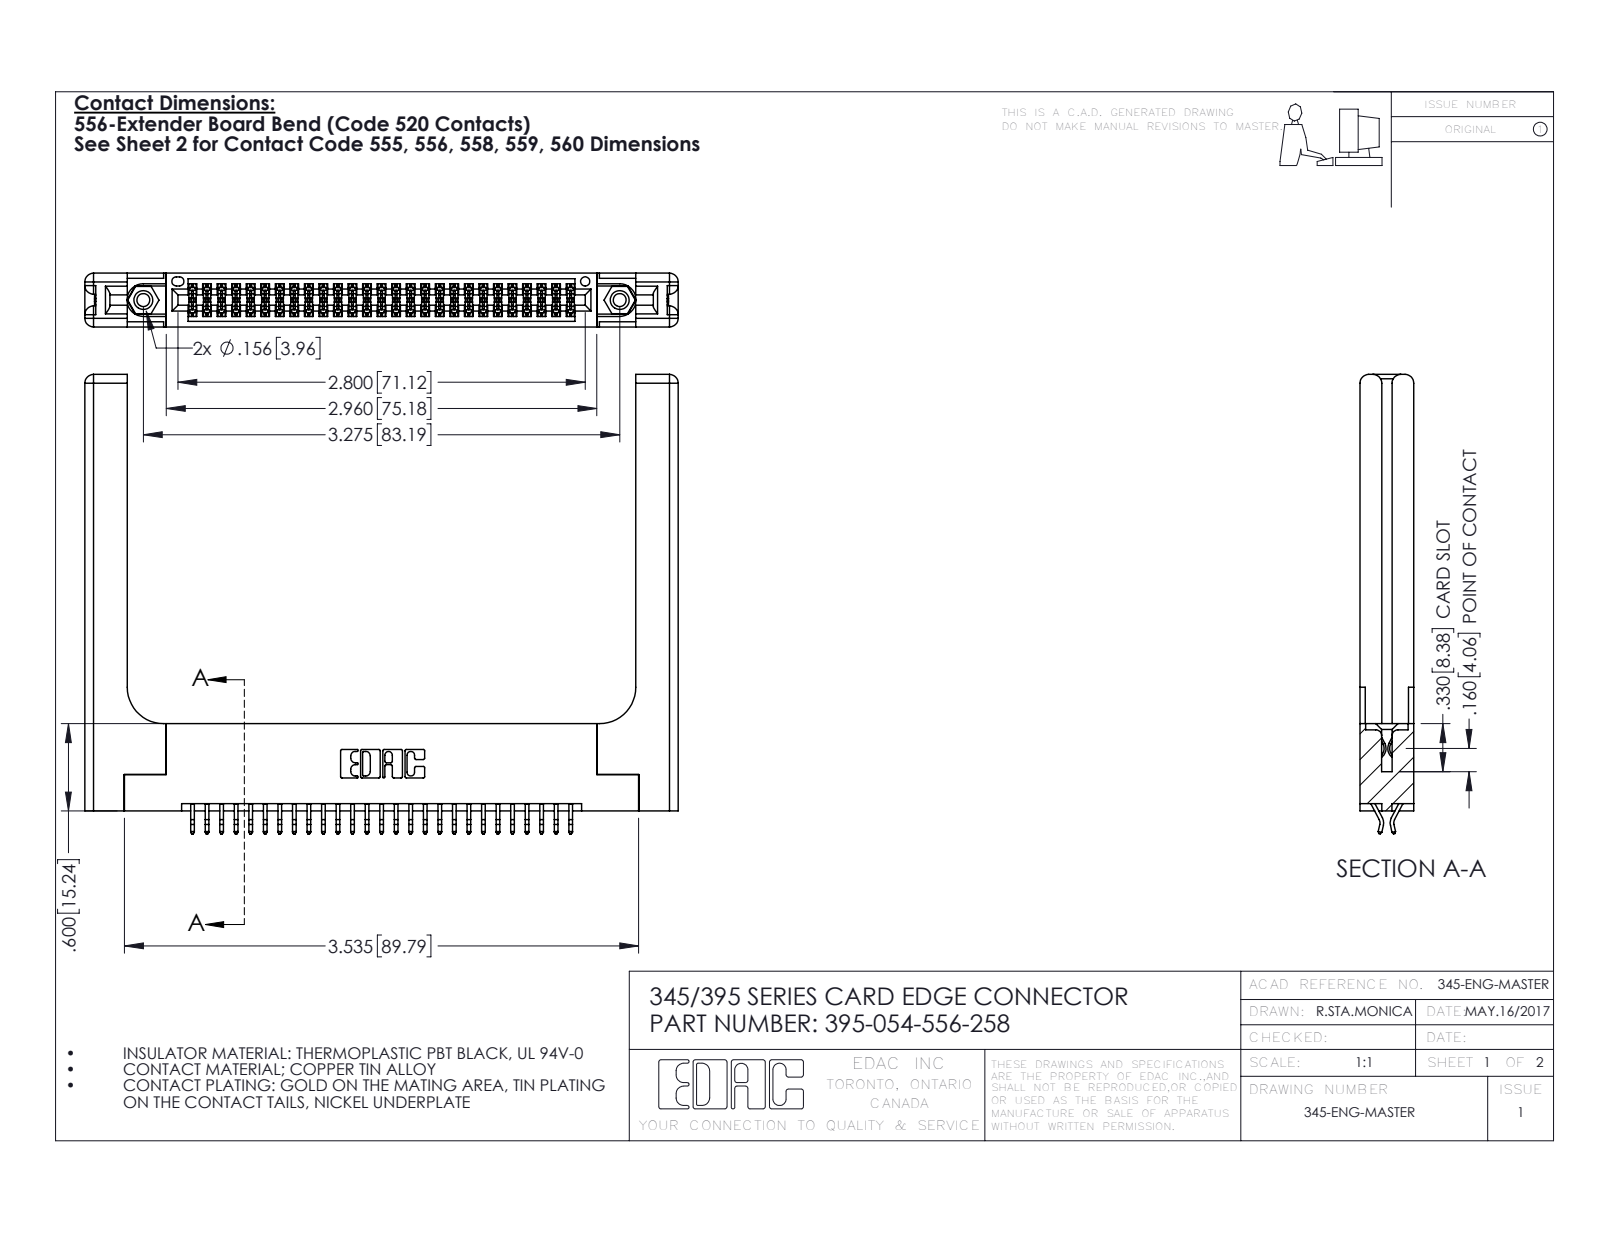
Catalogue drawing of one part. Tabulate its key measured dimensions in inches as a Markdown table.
| quantity | value |
| --- | --- |
| part name | 345 Part_Flush Mounting Lugs - 0.156 Dia-TH; 345-292-001_556 Tail; 345-220-058_345-220-058; 345-250-001_345-250-001-102 (+1 more) |
| STEP written by | SolidWorks 2016 (CONFIG_CONTROL_DESIGN) |
| units | inches |
| bodies | 59 solids, 3406 faces (2226 planar, 1120 cylindrical, 60 other) |
| overall size | 4.079 × 3.157 × 0.37 |
| volume | 1.123 in³ |
| surface area | 30.05 in² |
| round holes (diameter × count) | 0.089 × 2, 0.125 × 2, 0.156 × 2, 0.064 × 1 |
| round bosses / shafts (diameter × count) | 0.155 × 2 |
| partial cylindrical surfaces (radius × count) | 0.006 × 81, 0.01 × 22, 0.06 × 16, 0.007 × 6, 0.031 × 6, 0.026 × 3, 0.01 × 2, 0.014 × 2 |
| main face-to-face distances | 0.37, 0.072, 0.298, 0.2, 0.025, 0.225, 0.148, 0.15, 0.098, 0.272 |
| hole center spacings | 0.27, 3.04, 3.275 |
